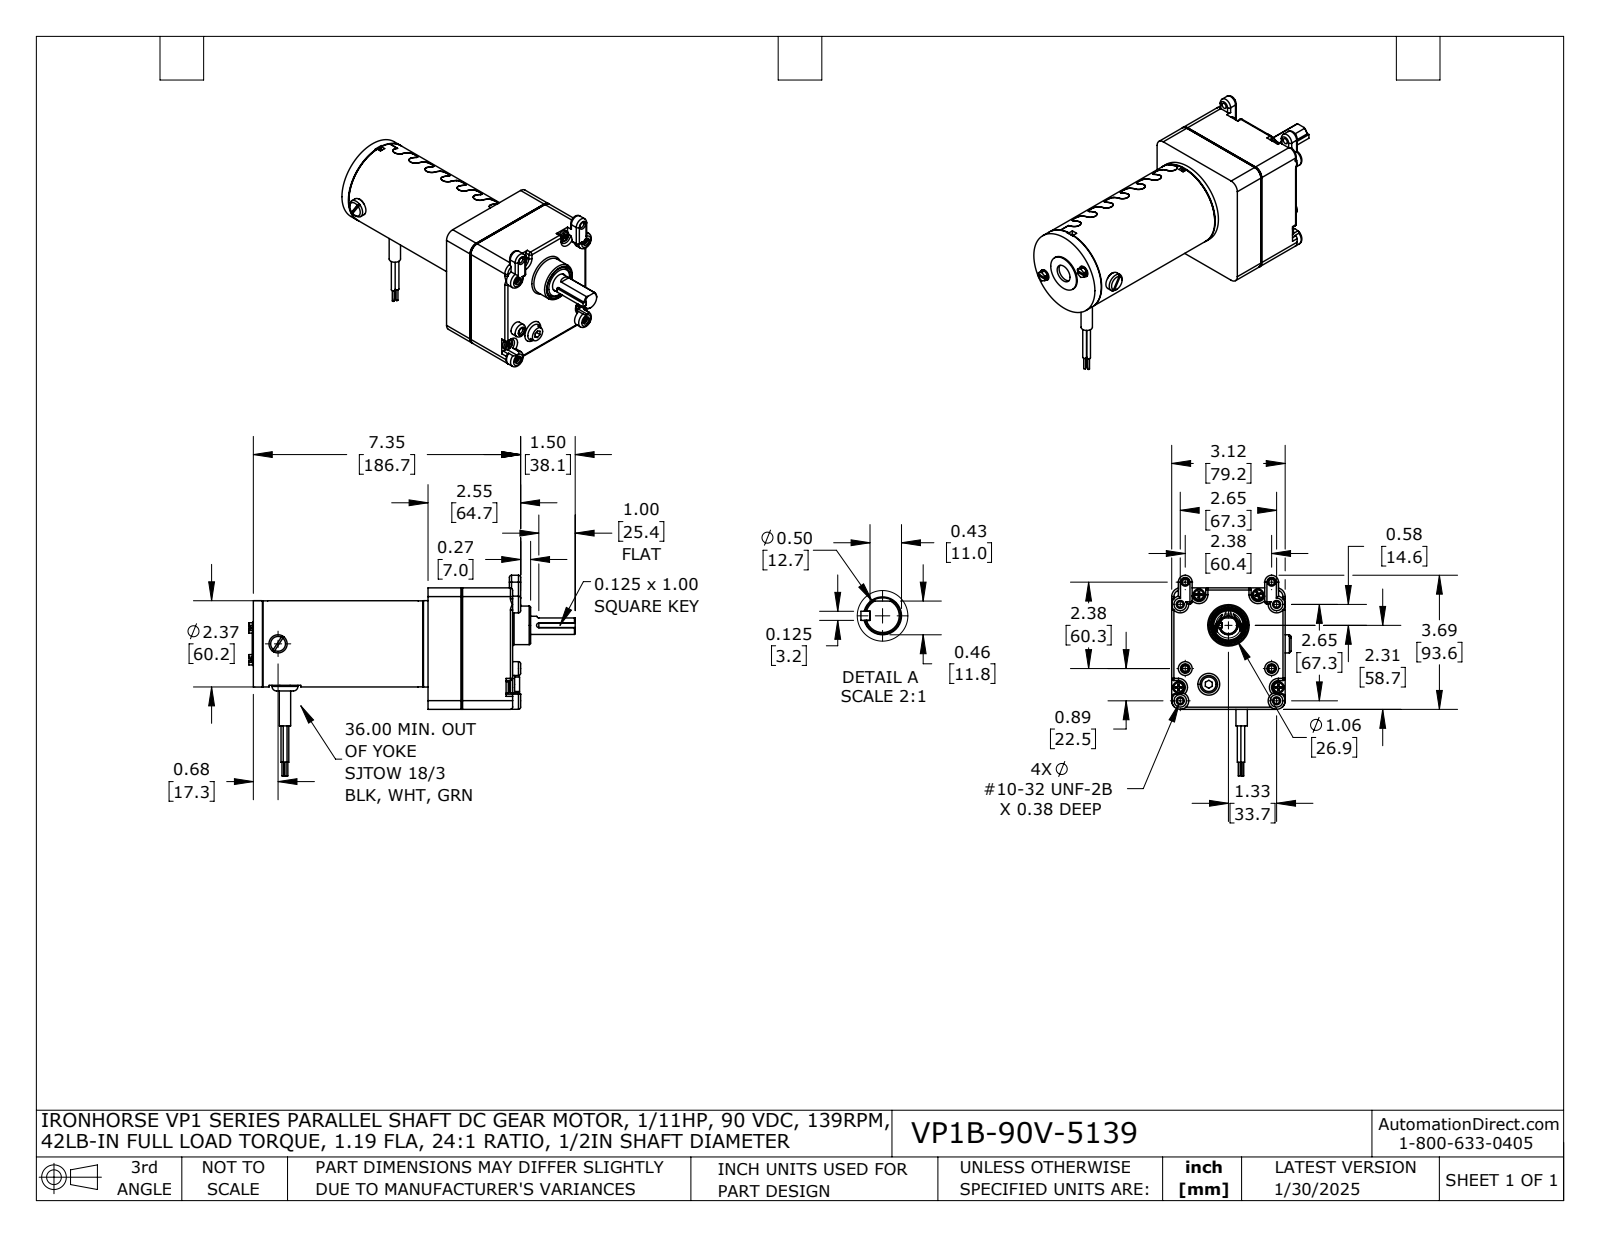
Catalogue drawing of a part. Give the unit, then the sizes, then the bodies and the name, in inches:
Units: inches
Overall size (bounding box): 8.974 × 5.516 × 3.283
Round holes (diameter × count): ⌀0.2 ×11, ⌀0.158 ×8, ⌀0.18 ×4, ⌀0.187 ×2, ⌀0.189 ×2, ⌀0.22 ×2, ⌀0.213 ×1, ⌀0.336 ×1, ⌀0.468 ×1, ⌀0.5 ×1, ⌀0.521 ×1, ⌀0.688 ×1
Round bosses / shafts (diameter × count): ⌀0.314 ×4, ⌀0.313 ×4, ⌀0.136 ×4, ⌀0.105 ×3, ⌀0.052 ×3, ⌀0.5 ×2, ⌀0.466 ×2, ⌀0.44 ×2
Partial cylindrical surfaces — rounded edges, fillets, slot ends (radius × count): R0.06 ×34, R0.062 ×21, R0.156 ×14, R0.151 ×7, R0.161 ×7, R0.15 ×6, R0.12 ×4, R0.235 ×4
Main face-to-face distances: 0.09, 3.12, 1.38, 2.326, 0.946, 0.106, 1.274, 2.22, 3.34, 0.315
Hole centre spacings: 1.68, 2.65, 1.074, 2.729, 3.093, 0.077, 0.297, 0.373
Volume: 12.28 in³ · Surface area: 225.5 in²
Bodies: 20 solids, 916 faces (340 planar, 422 cylindrical, 154 other)
Part name (STEP PRODUCT): VP1B-90V-5139
STEP written by: SolidWorks 2021 (AUTOMOTIVE_DESIGN)
